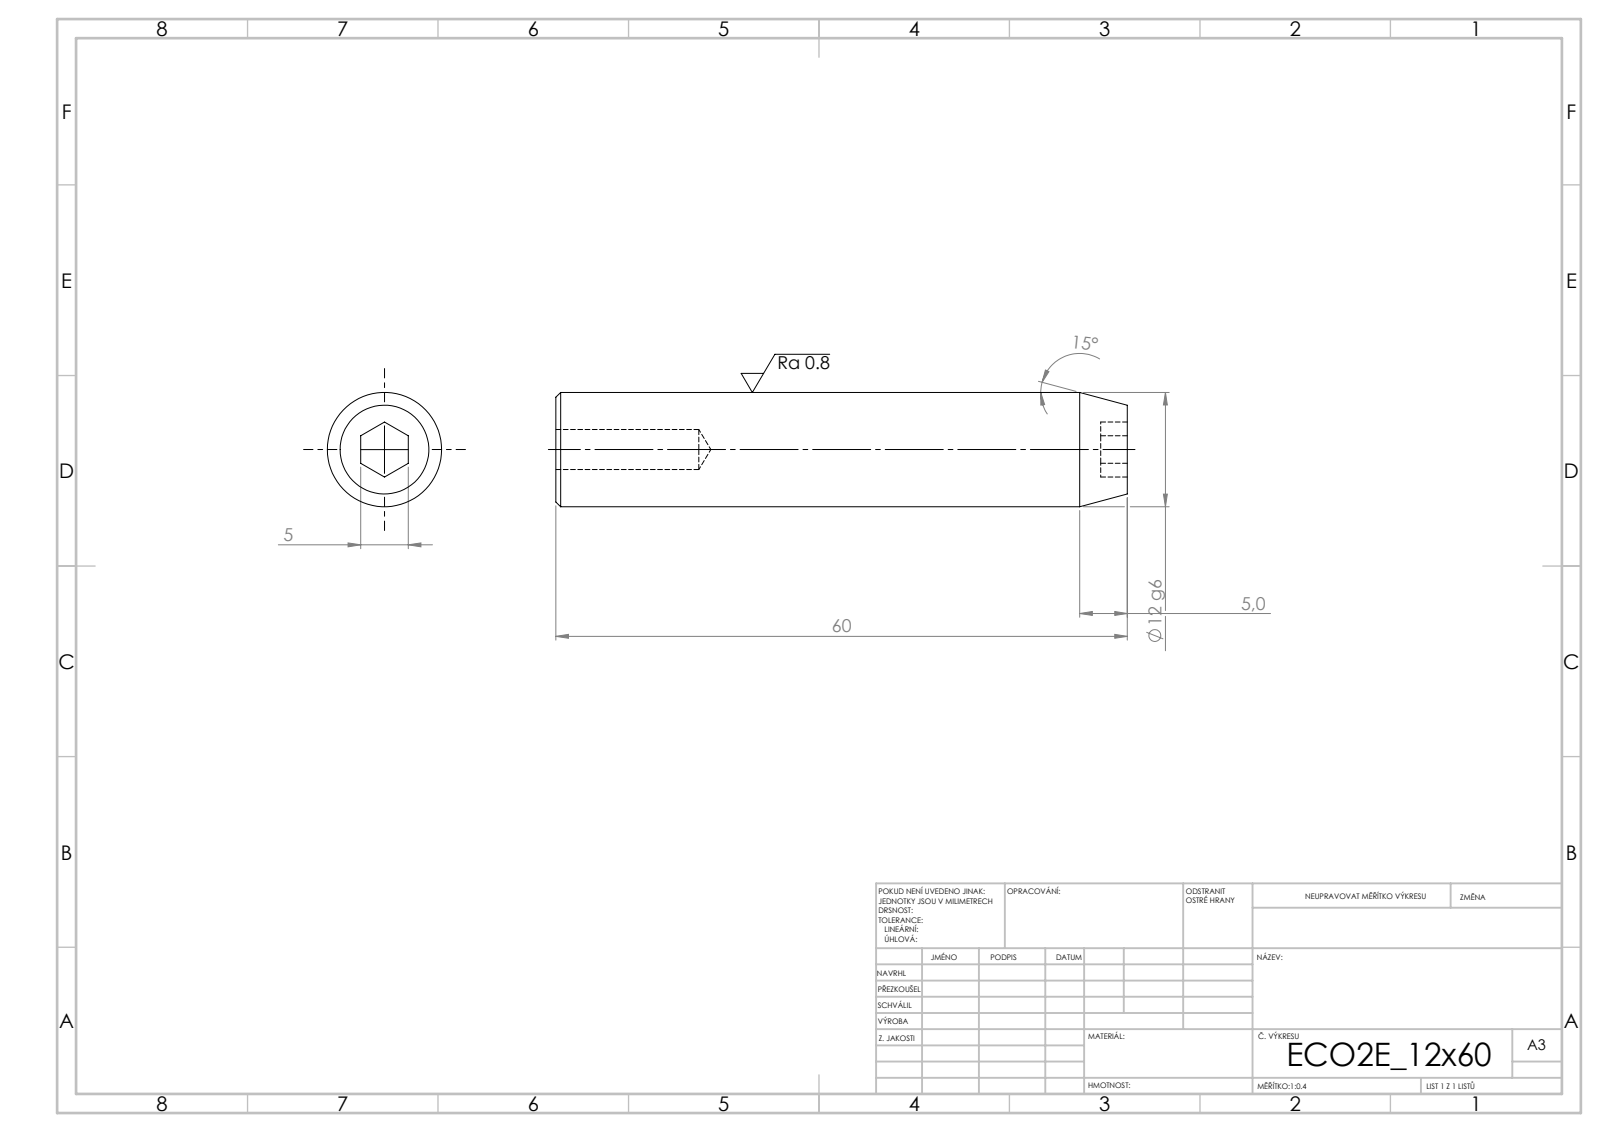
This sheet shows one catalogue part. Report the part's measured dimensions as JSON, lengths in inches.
{"step_written_by": "SolidWorks 2019 (CONFIG_CONTROL_DESIGN)", "units": "inches", "bodies": {"solids": 1, "faces": 19, "planar": 9, "cylindrical": 4, "other": 6}, "overall_size": [2.362, 0.472, 0.472], "volume_in3": 0.39, "surface_area_in2": 4.131, "round_holes": [[0.165, 1]], "round_bosses_or_shafts": [[0.472, 1]], "face_to_face_distances": [2.362, 0.197, 0.11, 2.252]}
